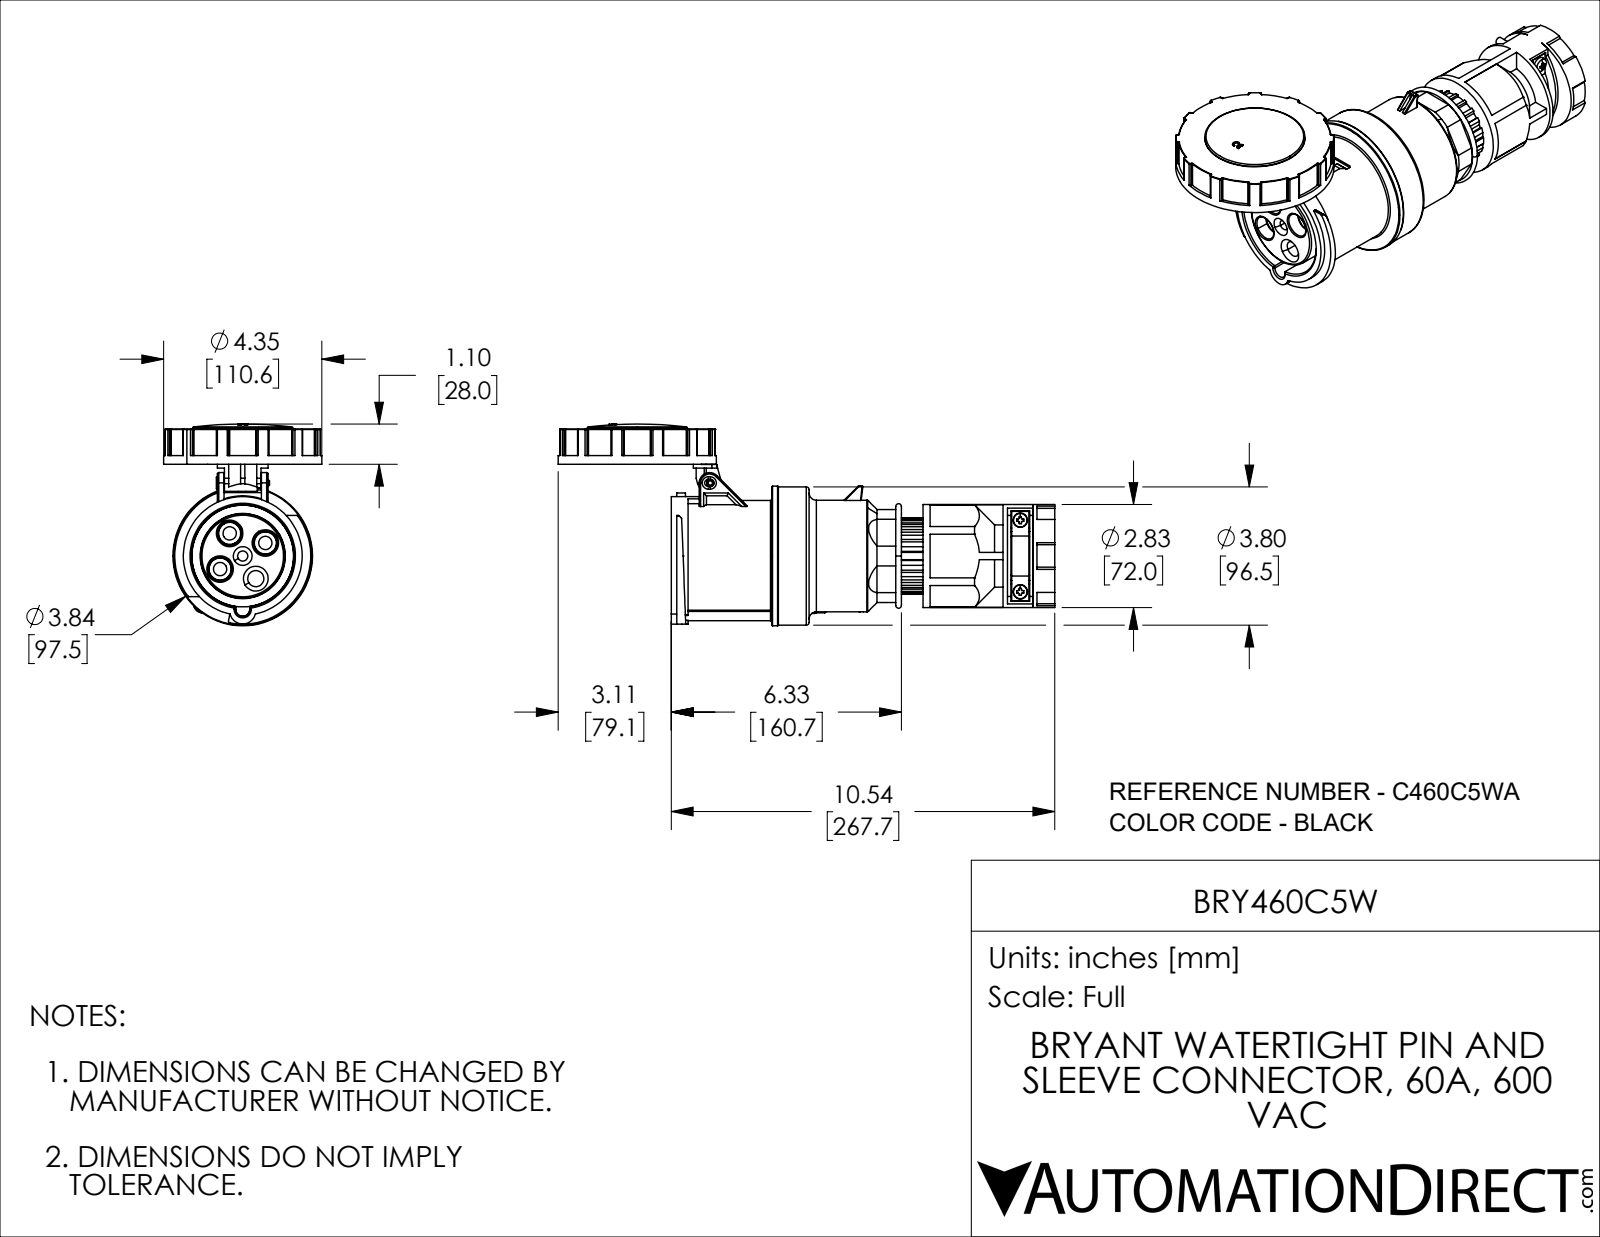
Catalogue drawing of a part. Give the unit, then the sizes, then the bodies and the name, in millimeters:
Units: millimetres
Overall size (bounding box): 346.77 × 140.9 × 110.55
Round holes (diameter × count): ⌀9.3 ×3, ⌀7.1 ×1, ⌀11.3 ×1, ⌀37 ×1, ⌀65.5 ×1, ⌀100.6 ×1
Round bosses / shafts (diameter × count): ⌀5 ×3, ⌀110.55 ×1, ⌀97.5 ×1, ⌀96.5 ×1, ⌀83 ×1, ⌀78 ×1, ⌀77.6 ×1, ⌀72 ×1
Partial cylindrical surfaces — rounded edges, fillets, slot ends (radius × count): R0.3 ×48, R1 ×40, R0.5 ×15, R34.5 ×6, R0.4 ×4, R2 ×4, R1.75 ×2, R2.5 ×2
Main face-to-face distances: 21.5, 3, 65, 26, 15.5, 92, 15, 161.5, 5, 164.5
Hole centre spacings: 18.24, 25.8, 36.49
Volume: 1 154 000 mm³ · Surface area: 181 813 mm²
Bodies: 2 solids, 1154 faces (477 planar, 395 cylindrical, 282 other)
Part name (STEP PRODUCT): BRY460C5W
STEP written by: SolidWorks 2021 (CONFIG_CONTROL_DESIGN)
